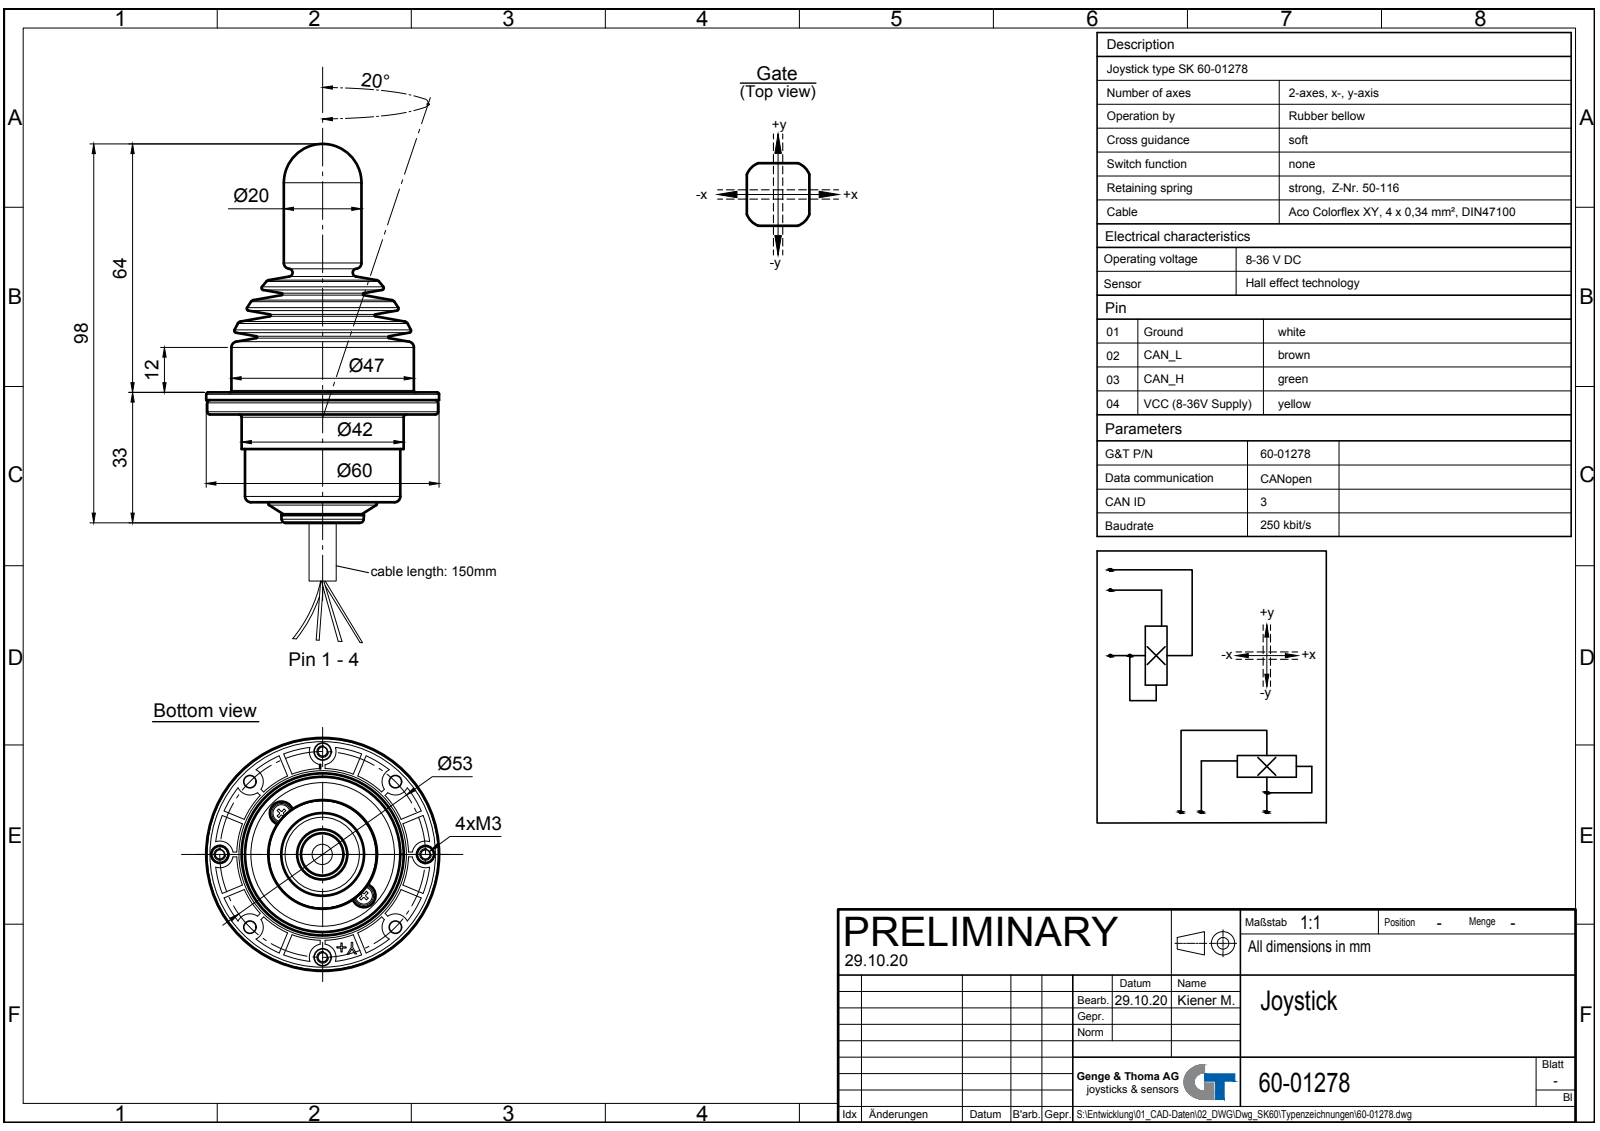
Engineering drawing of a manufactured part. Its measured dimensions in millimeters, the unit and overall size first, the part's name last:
Units: millimetres
Overall size (bounding box): 127.3 × 60 × 60
Round holes (diameter × count): ⌀3.2 ×8, ⌀2.46 ×4, ⌀3 ×4, ⌀6 ×1, ⌀10.9 ×1
Round bosses / shafts (diameter × count): ⌀1.5 ×4, ⌀0.8 ×4, ⌀60 ×1, ⌀59.5 ×1, ⌀47 ×1, ⌀44.25 ×1, ⌀41.75 ×1, ⌀40 ×1
Partial cylindrical surfaces — rounded edges, fillets, slot ends (radius × count): R3.45 ×8, R27.75 ×1
Main face-to-face distances: 2.95, 2.45, 5.4, 22.6, 25.05, 28, 1.25, 1.7, 26.3, 3.7
Hole centre spacings: 20.28, 26.5, 37.48, 48.97, 53
Volume: 93 334 mm³ · Surface area: 19 906 mm²
Bodies: 1 solid, 234 faces (103 planar, 82 cylindrical, 49 other)
Part name (STEP PRODUCT): 60-01162
STEP written by: Autodesk Inventor 2017 (AP242_MANAGED_MODEL_BASED_3D_ENGINEERING_MIM_LF)
